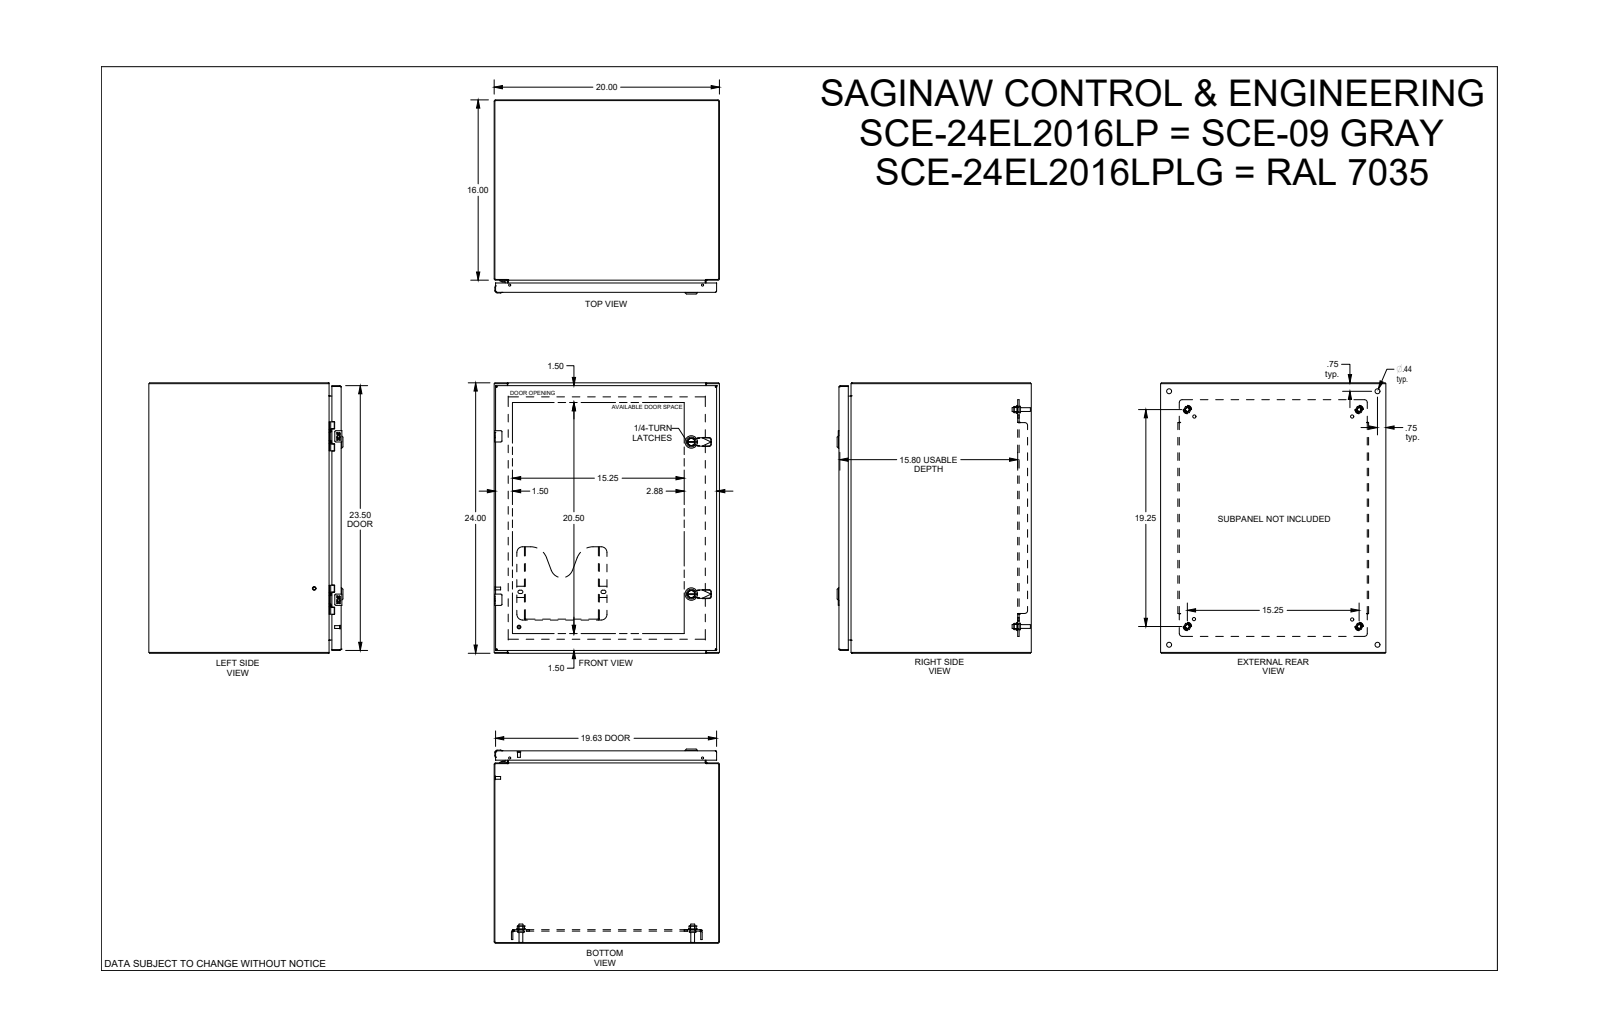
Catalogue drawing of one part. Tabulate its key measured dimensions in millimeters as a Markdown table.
| quantity | value |
| --- | --- |
| part name | SCE-24EL2016LP |
| STEP written by | SolidWorks 2021 (AUTOMOTIVE_DESIGN) |
| units | millimeters |
| bodies | 45 solids, 2787 faces (1089 planar, 840 cylindrical, 858 other) |
| overall size | 609.6 × 508 × 437.6 |
| volume | 4 131 000 mm³ |
| surface area | 4 017 000 mm² |
| round holes (diameter × count) | 4.4 × 4, 5.2 × 4, 6.2 × 4, 6.8 × 4, 7.1 × 4, 9.3 × 4, 9.5 × 4, 11.1 × 4, 12.7 × 4, 1 × 2, 4.8 × 2, 5 × 2 |
| round bosses / shafts (diameter × count) | 4.3 × 6, 9.3 × 4, 8.4 × 4, 6.4 × 4, 6.3 × 4, 6.1 × 4, 5 × 3, 28 × 2 |
| partial cylindrical surfaces (radius × count) | 0.3 × 56, 0.3 × 28, 0.4 × 24, 0.5 × 20, 1 × 17, 1.5 × 13, 0.7 × 12, 2.5 × 12 |
| main face-to-face distances | 1.9, 506.1, 607.7, 1.5, 430.2, 433.7, 431.7, 432.1, 508, 504.2 |
| hole center spacings | 25, 368.3, 22.2, 531.8, 681.8, 0.5, 12.5, 12.5 |
